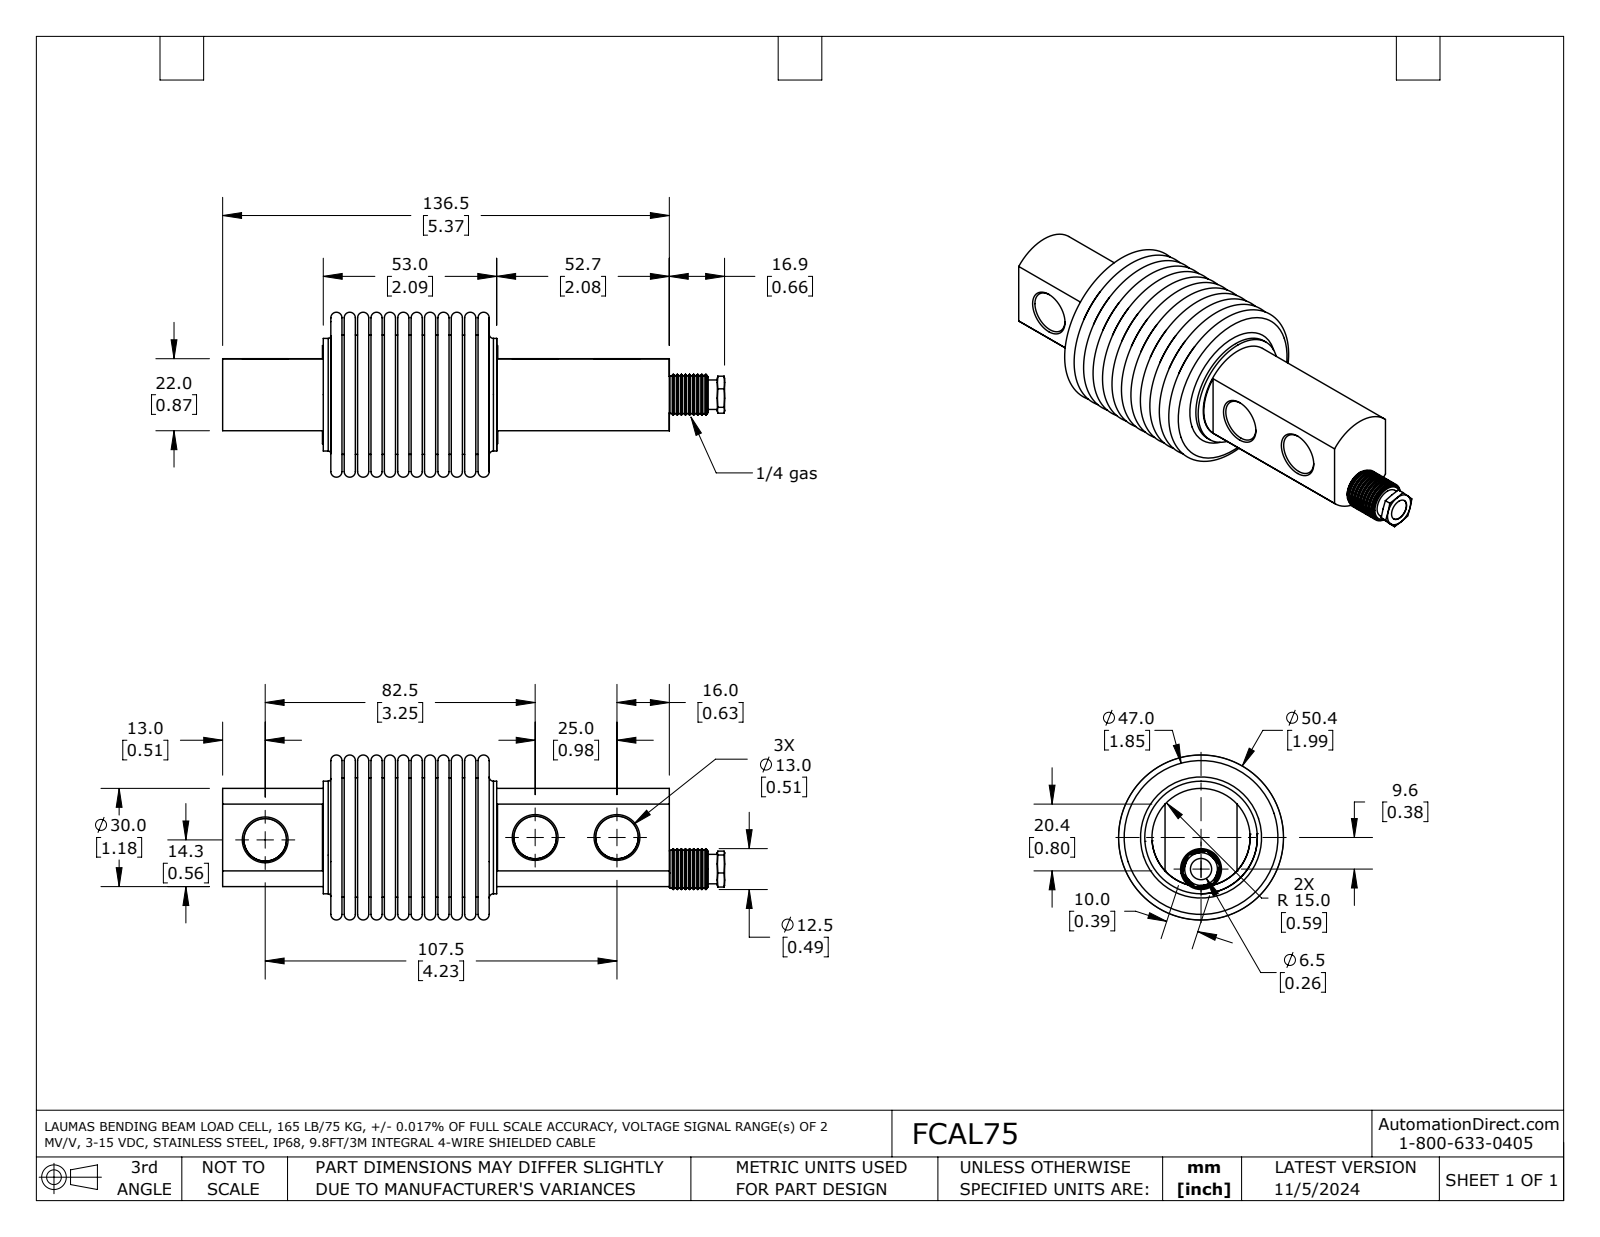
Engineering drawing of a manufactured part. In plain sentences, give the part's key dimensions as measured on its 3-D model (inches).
The part is named "FCAL75". Its 3-D file was written by "SolidWorks 2021 (AUTOMOTIVE_DESIGN)". It is 2 solids with 378 faces: 32 planar, 30 cylindrical and 316 other. Overall it measures 6.039 by 1.984 by 1.984 inches. Its volume is 5.302 cubic inches and its surface area 117.2 square inches. Round holes: 3 of diameter 0.512, 1 of diameter 0.256, 1 of diameter 0.394. Round bosses or shafts: 1 of diameter 1.354, 1 of diameter 1.339, 1 of diameter 1.181, 1 of diameter 0.453, 1 of diameter 0.354. The main face-to-face distances are 1.897, 0.866, 1.889, 1.905, 4.072, 4.065, 2.175, 2.167, 1.302, 1.309. The hole center spacings are 0.984, 3.248, 4.232.
